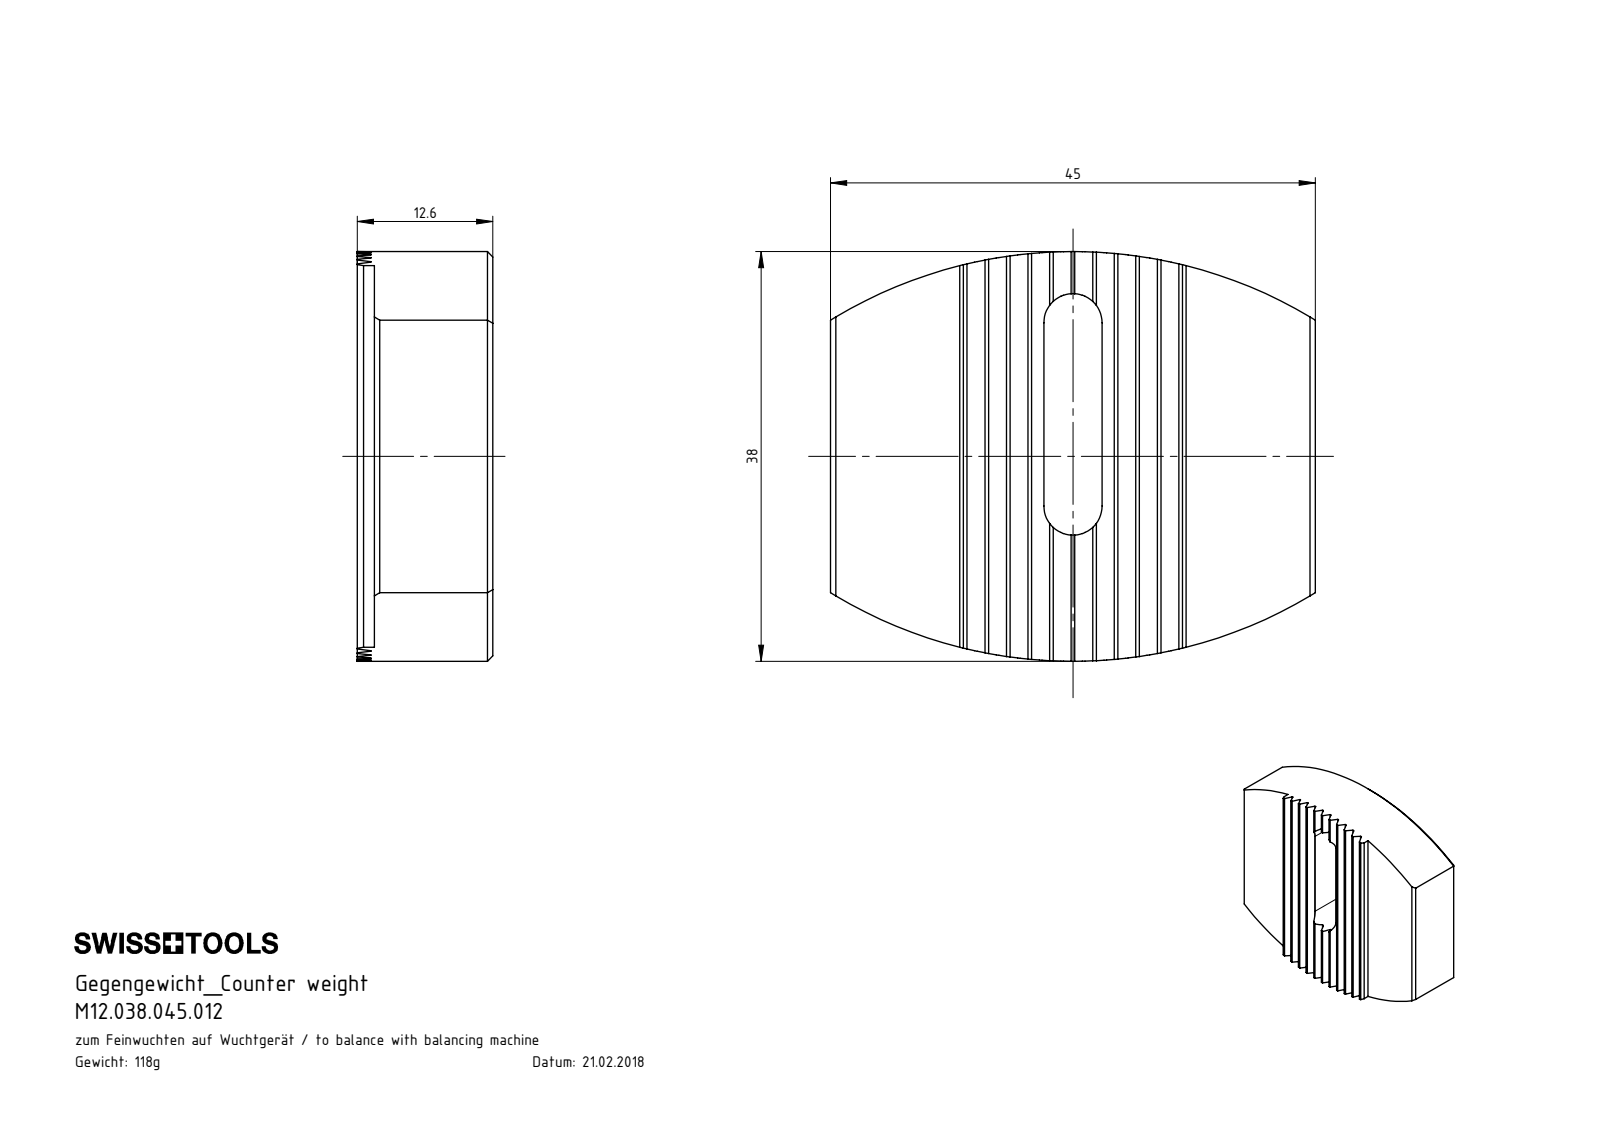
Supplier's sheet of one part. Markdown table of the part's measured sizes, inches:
| quantity | value |
| --- | --- |
| part name | BV2.ER1.001.012 |
| STEP written by | SolidWorks 2017 (AUTOMOTIVE_DESIGN) |
| units | inches |
| bodies | 1 solid, 76 faces (56 planar, 18 cylindrical, 2 other) |
| overall size | 1.772 × 1.496 × 0.495 |
| volume | 0.92 in³ |
| surface area | 8.792 in² |
| partial cylindrical surfaces (radius × count) | 0.006 × 10, 0.106 × 2, 0.226 × 2, 1.693 × 2 |
| main face-to-face distances | 0.433, 0.068, 0.205, 0.341, 0.136, 0.409, 0.273, 0.477, 1.772, 0.204 |
